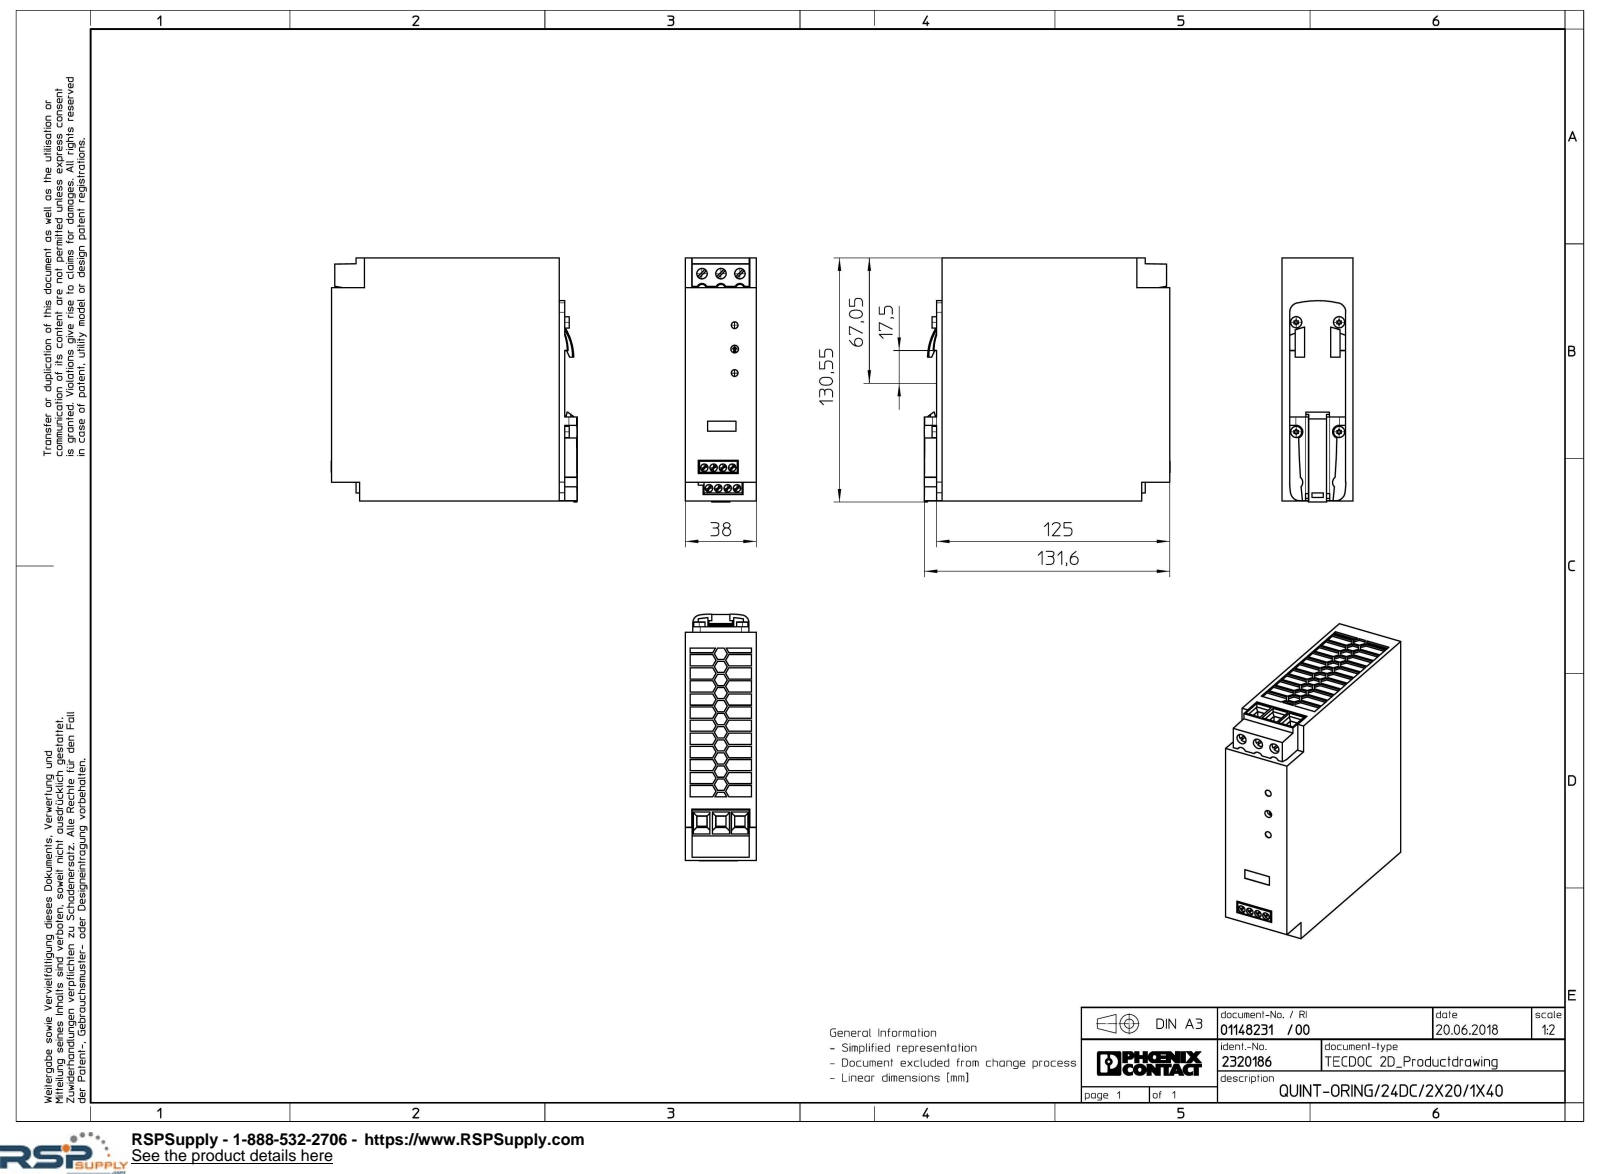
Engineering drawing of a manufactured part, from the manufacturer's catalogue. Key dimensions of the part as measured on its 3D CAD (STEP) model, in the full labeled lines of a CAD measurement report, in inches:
Part name (STEP PRODUCT): QUINT_ORING_24DC_2X20_1X40-select
STEP written by: Creo Elements/Direct Modeling 20.1A 29-Sep-2018 (C) Parametric Technology GmbH (AUTOMOTIVE_DESIGN)
Units: inches
Bodies: 1 solid, 957 faces (844 planar, 106 cylindrical, 7 other)
Overall size (bounding box): 5.189 × 5.14 × 1.496
Volume: 36.59 in³ · Surface area: 95.09 in²
Round holes (diameter × count): ⌀0.157 ×8, ⌀0.22 ×3, ⌀0.142 ×2, ⌀0.161 ×1
Round bosses / shafts (diameter × count): ⌀0.236 ×4
Partial cylindrical surfaces — rounded edges, fillets, slot ends (radius × count): R0.004 ×48, R0.138 ×4, R0.197 ×4, R0.108 ×3, R0.157 ×2, R1.181 ×2, R1.575 ×2, R15.807 ×2
Main face-to-face distances: 1.496, 0.039, 5.079, 0.118, 5.039, 4.921, 4.803, 5.118, 0.138, 0.591
Hole centre spacings: 0.197, 0.394, 0.444, 0.444, 0.525, 0.4, 0.504, 0.523
